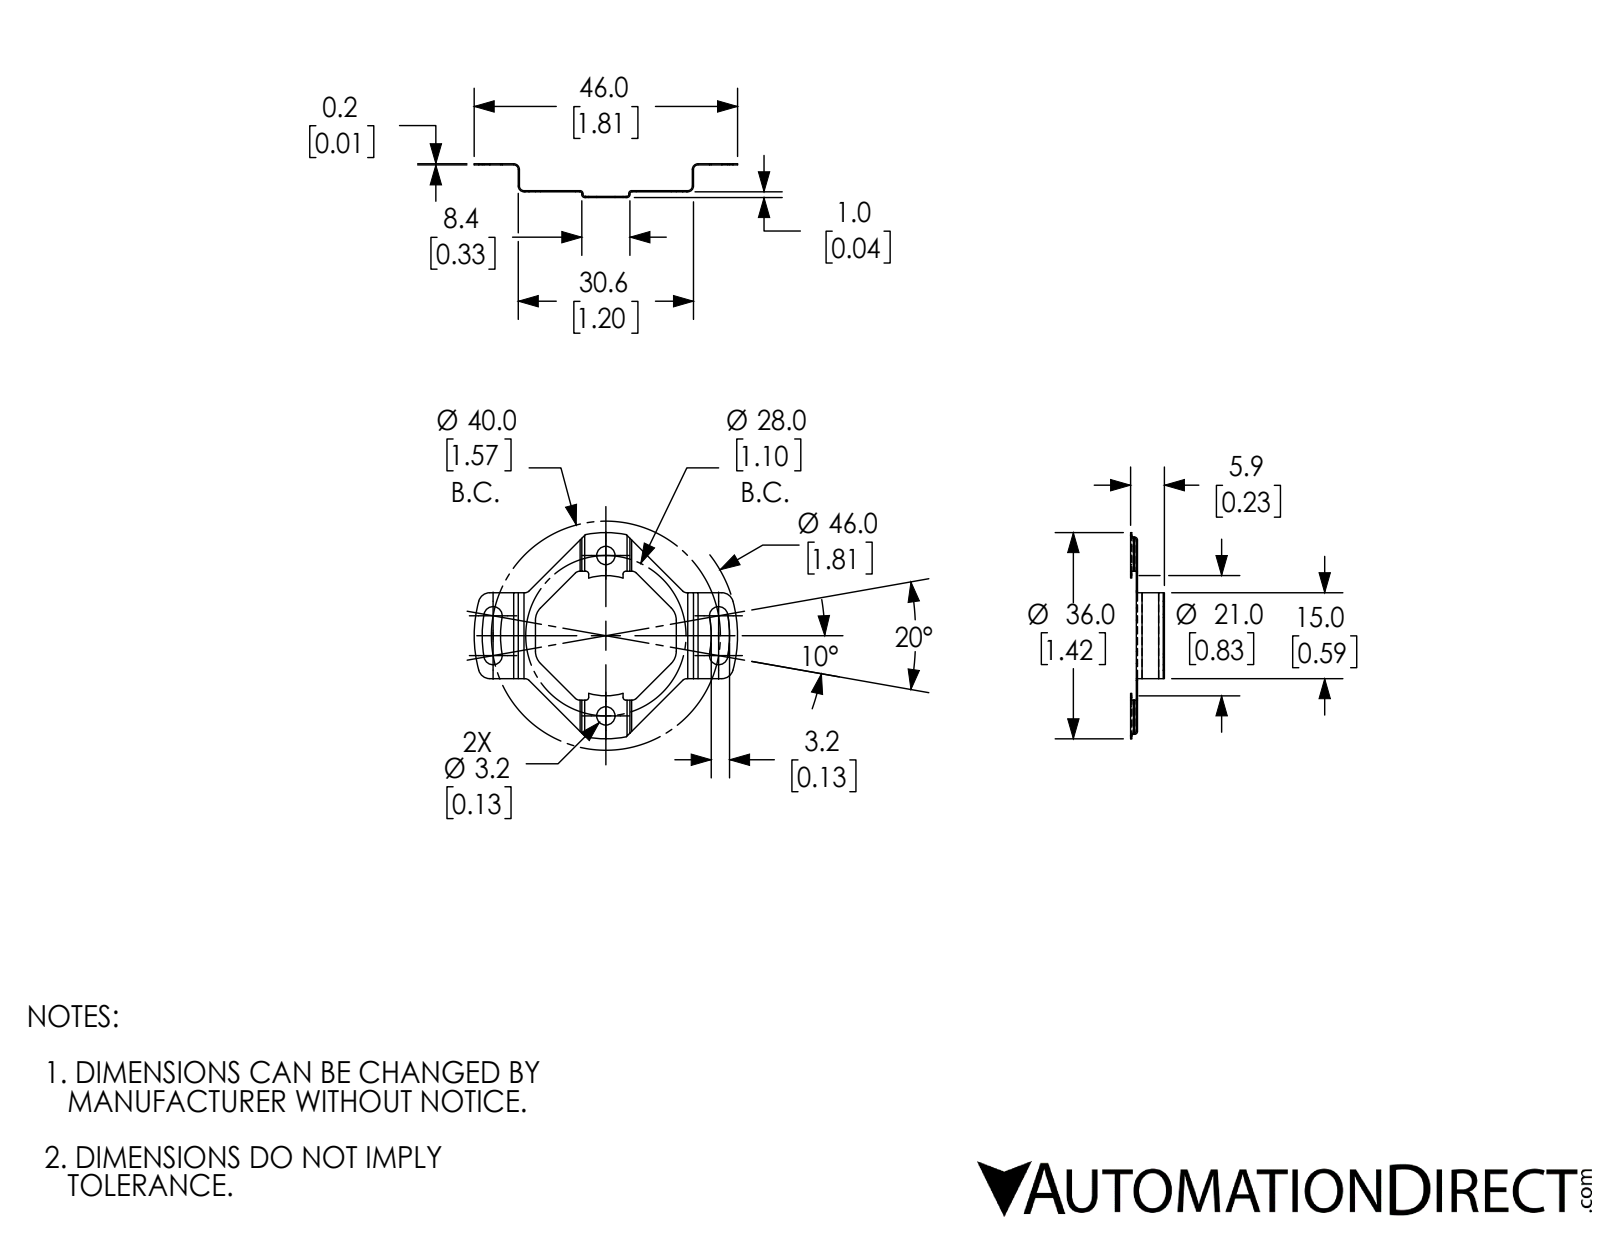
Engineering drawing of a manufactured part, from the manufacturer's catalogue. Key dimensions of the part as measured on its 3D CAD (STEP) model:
Part name (STEP PRODUCT): TRD-SHR-40
STEP written by: SolidWorks 2017 (AUTOMOTIVE_DESIGN)
Units: inches
Bodies: 1 solid, 111 faces (46 planar, 65 cylindrical, 0 other)
Overall size (bounding box): 1.811 × 1.417 × 0.232
Volume: 0.008 in³ · Surface area: 2.112 in²
Round holes (diameter × count): ⌀0.126 ×2
Partial cylindrical surfaces — rounded edges, fillets, slot ends (radius × count): R0.039 ×12, R0.02 ×8, R0.012 ×4, R0.031 ×4, R0.063 ×4, R0.079 ×4, R0.118 ×4, R0.413 ×1
Main face-to-face distances: 0.185, 0.039, 0.224, 0.177, 0.193, 0.047, 0.232, 0.217, 0.031, 1.197
Hole centre spacings: 1.102
